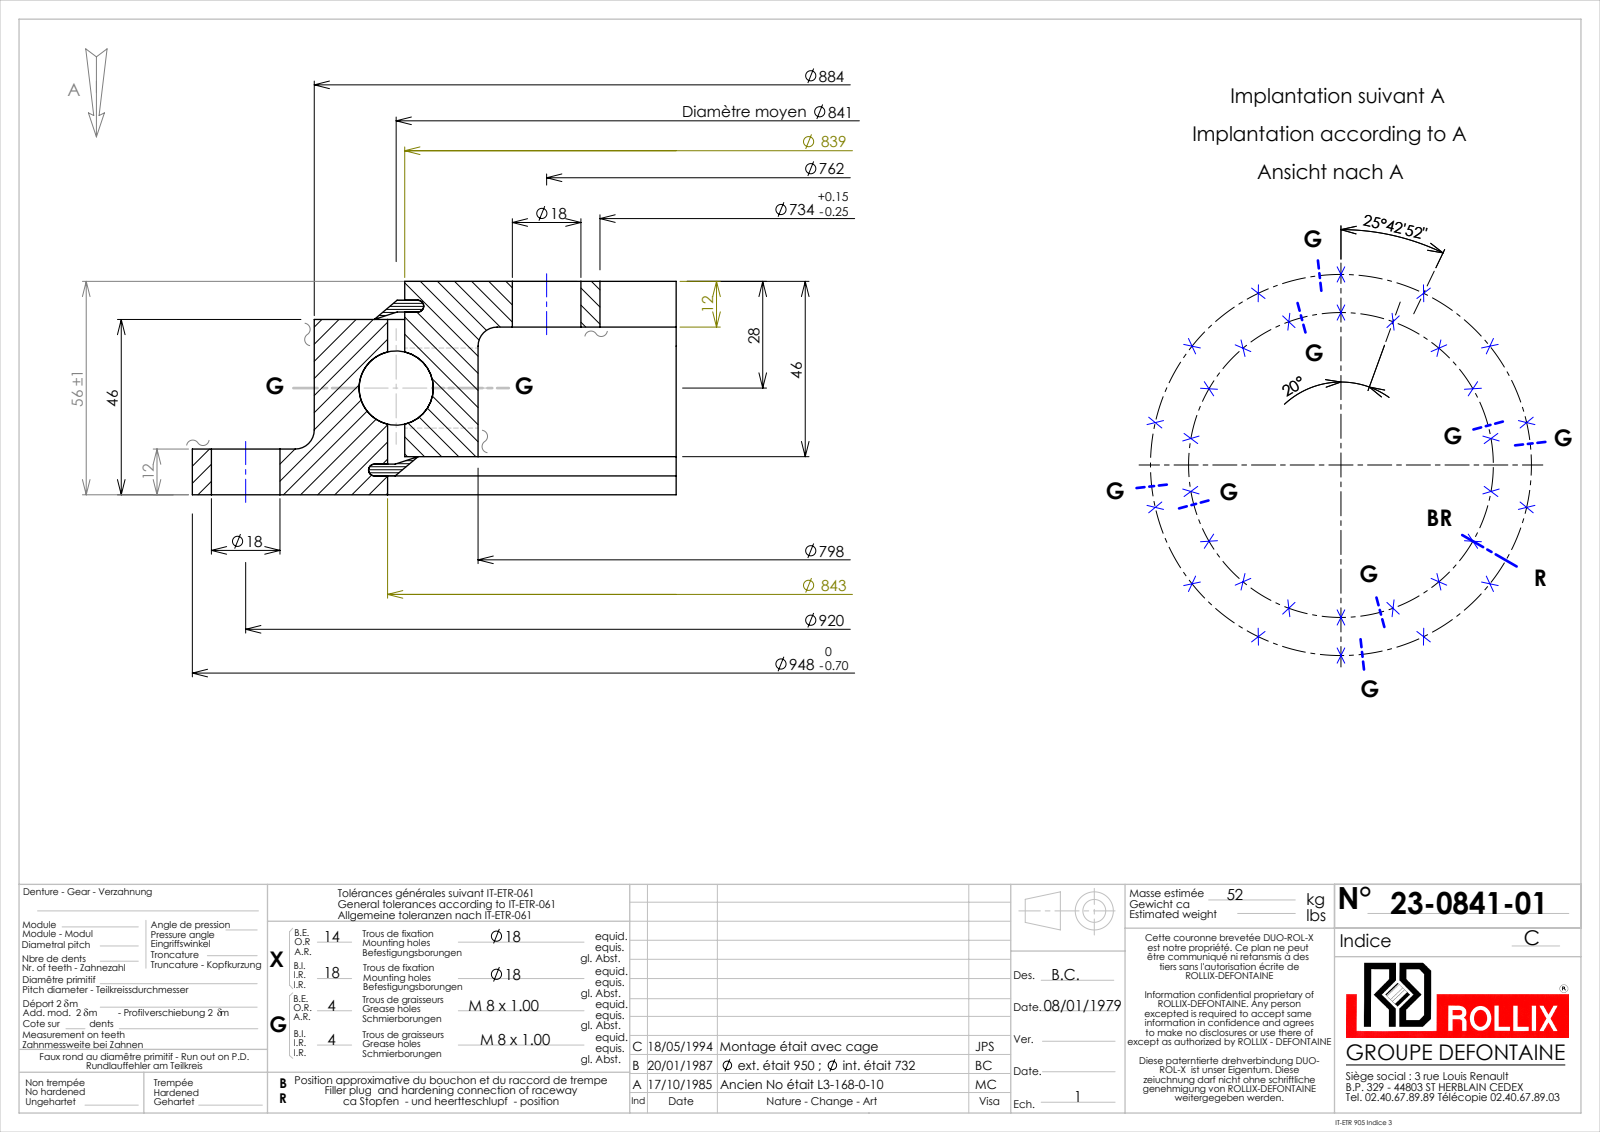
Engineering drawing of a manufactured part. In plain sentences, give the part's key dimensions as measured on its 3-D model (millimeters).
The part is named "23-0841-01". Its 3-D file was written by "SolidWorks 2016 (CONFIG_CONTROL_DESIGN)". It is 13 solids with 322 faces: 94 planar, 116 cylindrical and 112 other. Overall it measures 948 by 948 by 56 millimeters. Its volume is 6 167 000 cubic millimeters and its surface area 1 270 000 square millimeters. Round holes: 32 of diameter 18, 8 of diameter 7, 1 of diameter 734, 1 of diameter 798, 1 of diameter 845.5. Round bosses or shafts: 8 of diameter 8, 1 of diameter 948, 1 of diameter 884, 1 of diameter 836.5. The main face-to-face distances are 12, 44, 56, 10, 46, 2, 34, 32, 36, 8.05. The hole center spacings are 381, 132.32, 260.62, 659.91, 489.8, 583.72, 750.42, 716.04.
